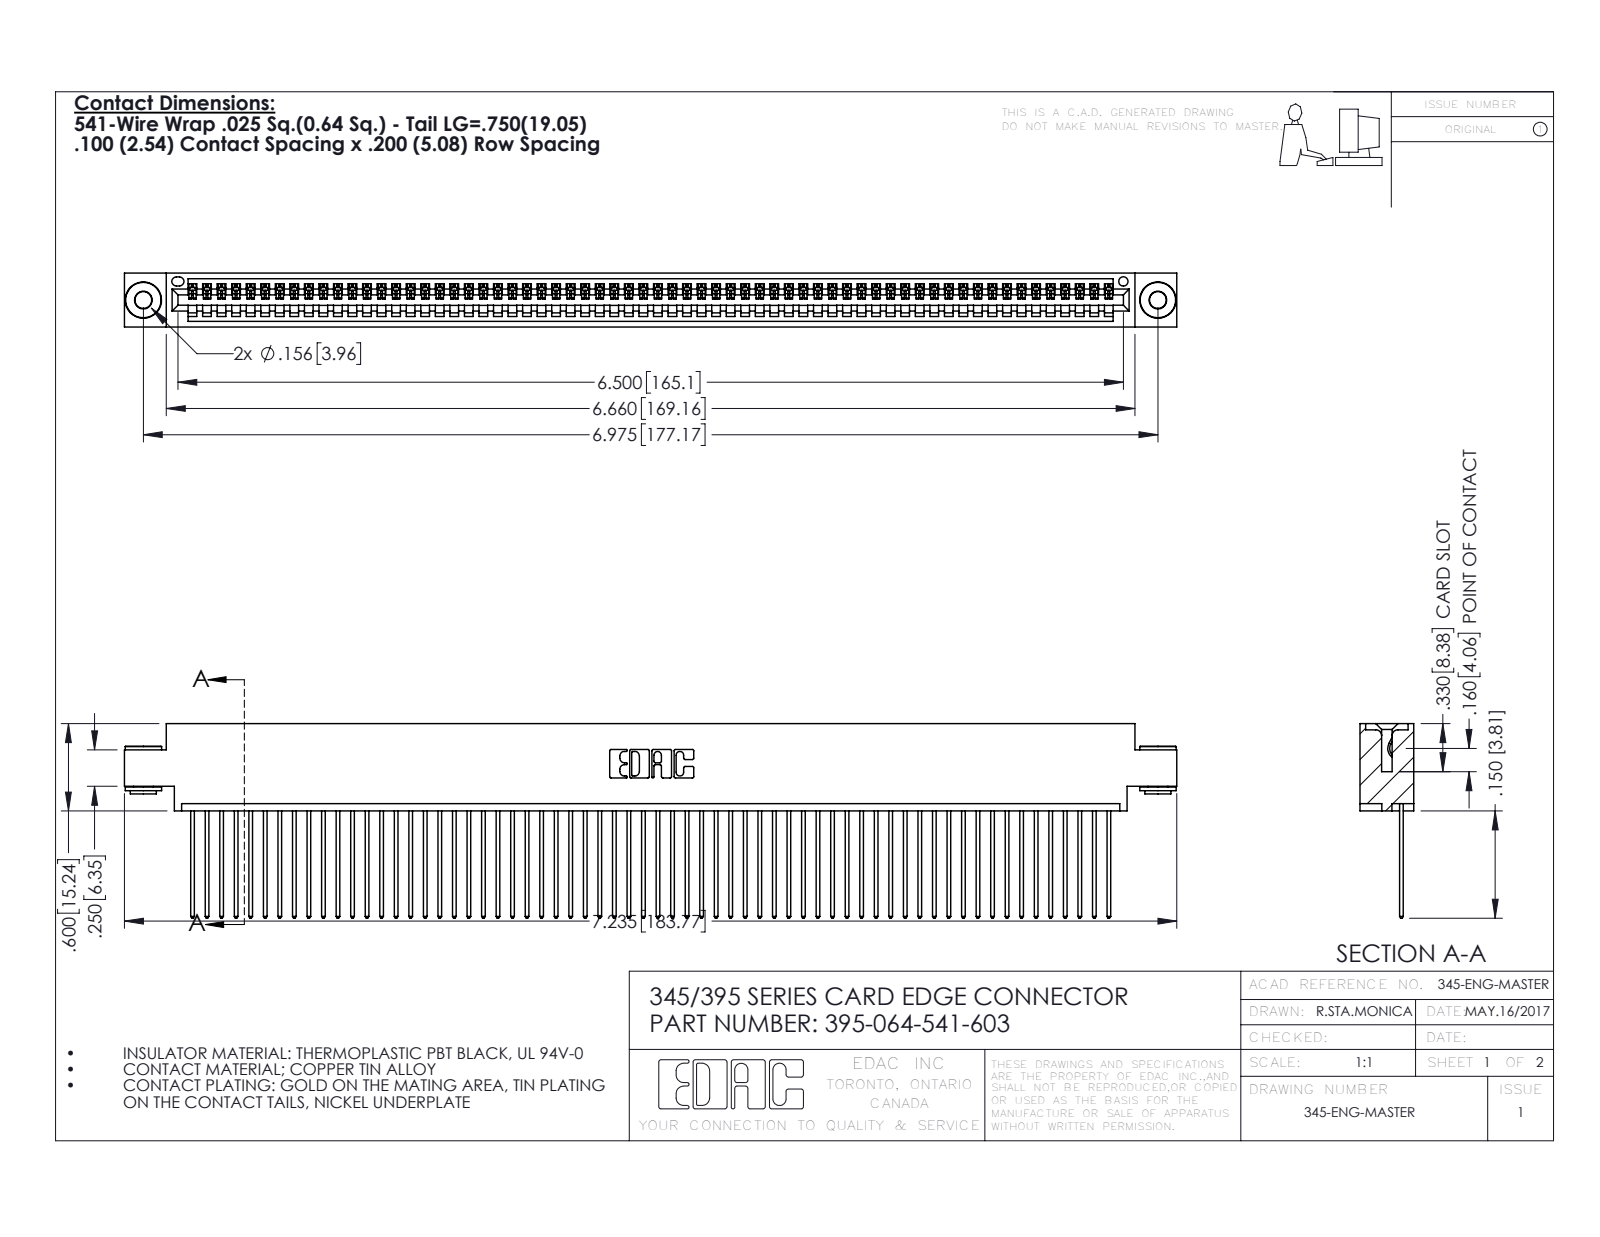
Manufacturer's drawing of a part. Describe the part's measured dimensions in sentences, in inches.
The part is named "345 Part_0.170 Offset - 0.156 Dia-TH; 395-064-541-603; 345-292-001_345-293-141; 345-250-002_345-250-002-102". Its 3-D file was written by "SolidWorks 2016 (CONFIG_CONTROL_DESIGN)". It is 67 solids with 3880 faces: 2654 planar, 1218 cylindrical and 8 other. Overall it measures 7.235 by 1.337 by 0.37 inches. Its volume is 1.083 cubic inches and its surface area 39.48 square inches. Round holes: 2 of diameter 0.116, 2 of diameter 0.156, 1 of diameter 0.064. Round bosses or shafts: 2 of diameter 0.25, 2 of diameter 0.18, 2 of diameter 0.136. Partial cylindrical surfaces (rounded edges, fillets, slot ends): 128 of radius 0.006, 128 of radius 0.01, 22 of radius 0.01, 6 of radius 0.007, 6 of radius 0.031, 3 of radius 0.026, 2 of radius 0.031, 2 of radius 0.04. The main face-to-face distances are 0.072, 0.298, 0.098, 0.272, 0.025, 0.37, 0.2, 0.225, 0.175, 0.149. The hole center spacings are 0.27, 6.739, 6.975.
